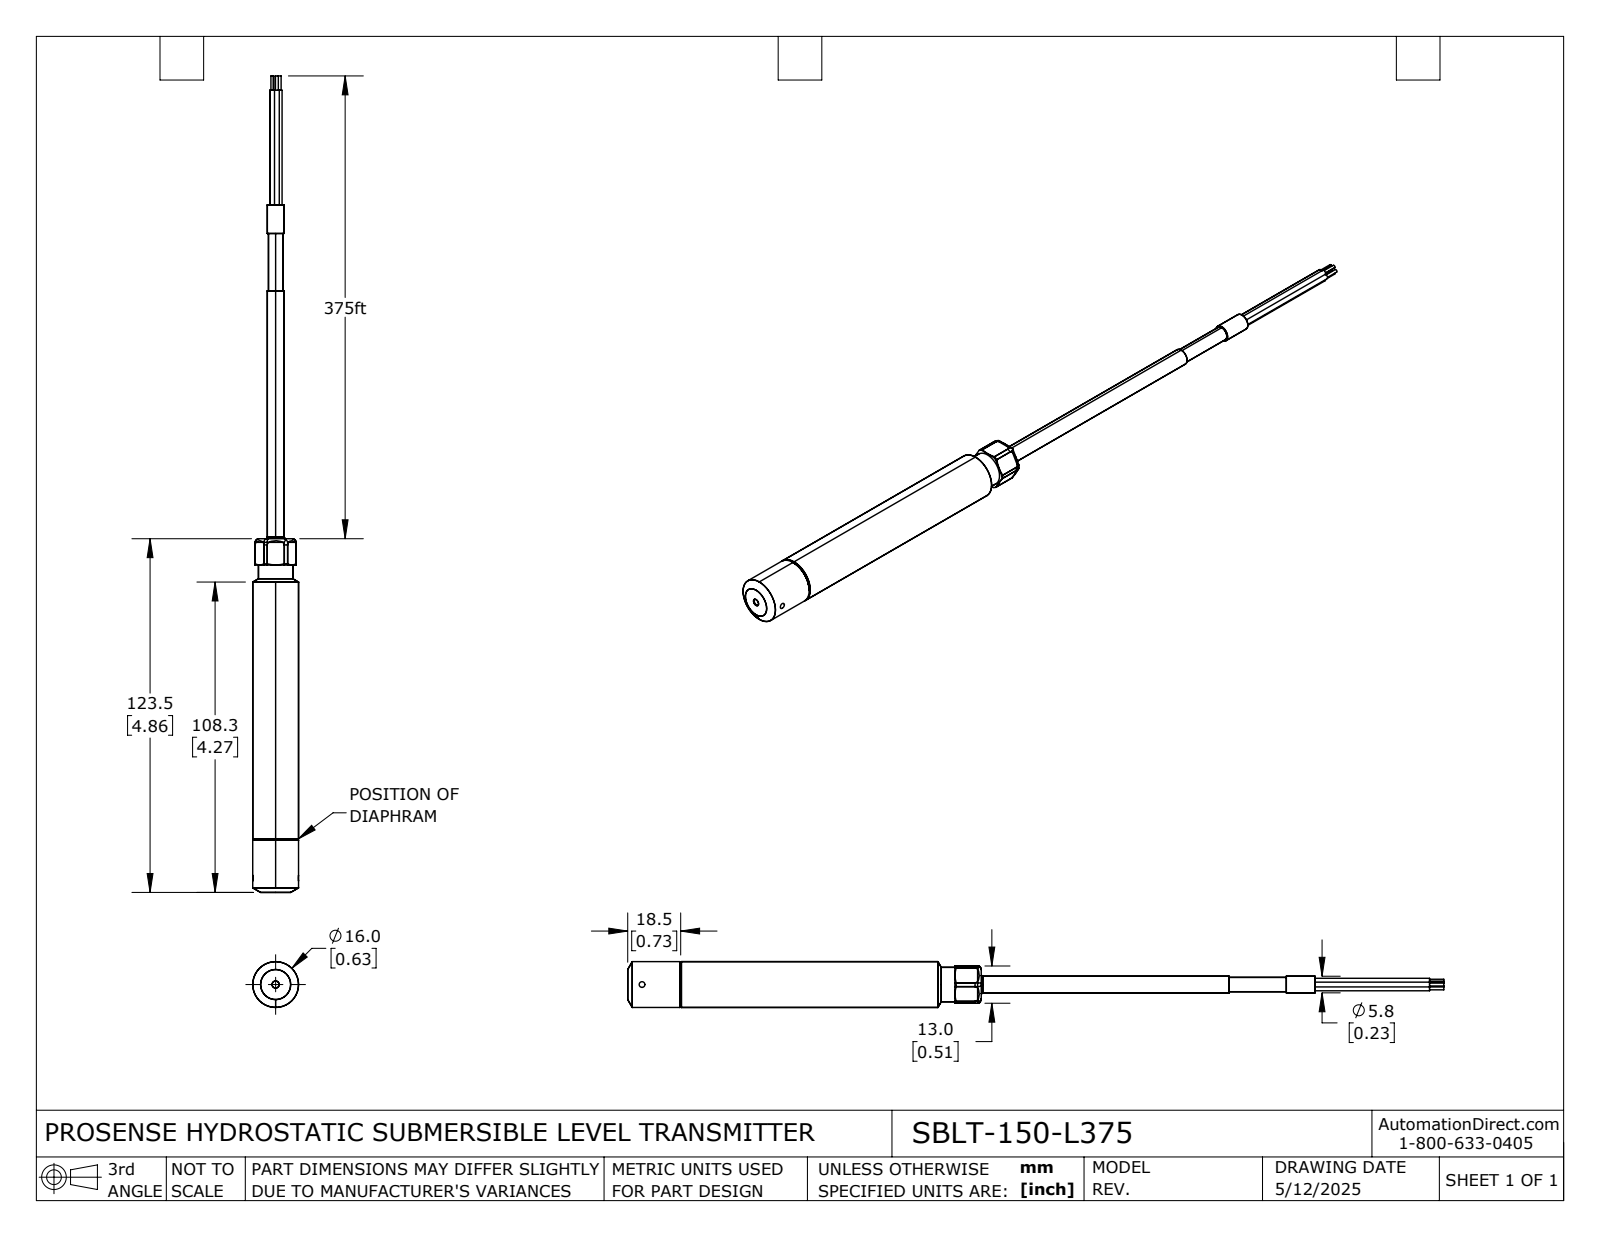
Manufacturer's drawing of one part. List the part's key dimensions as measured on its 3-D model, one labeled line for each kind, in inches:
Part name (STEP PRODUCT): SBLT-150-L375
STEP written by: SolidWorks 2024 (AUTOMOTIVE_DESIGN)
Units: inches
Bodies: 11 solids, 201 faces (52 planar, 88 cylindrical, 61 other)
Overall size (bounding box): 11.221 × 0.63 × 0.63
Volume: 3.198 in³ · Surface area: 29.94 in²
Round holes (diameter × count): ⌀0.079 ×1, ⌀0.098 ×1, ⌀0.374 ×1, ⌀0.516 ×1, ⌀0.551 ×1
Round bosses / shafts (diameter × count): ⌀0.066 ×5, ⌀0.039 ×5, ⌀0.63 ×1, ⌀0.629 ×1, ⌀0.472 ×1, ⌀0.472 ×1, ⌀0.244 ×1, ⌀0.228 ×1
Partial cylindrical surfaces — rounded edges, fillets, slot ends (radius × count): R0.05 ×6, R0.281 ×1
Main face-to-face distances: 0.512, 4.861, 4.33, 0.531, 4.589, 8.918, 9.45, 3.77, 0.197, 8.721
